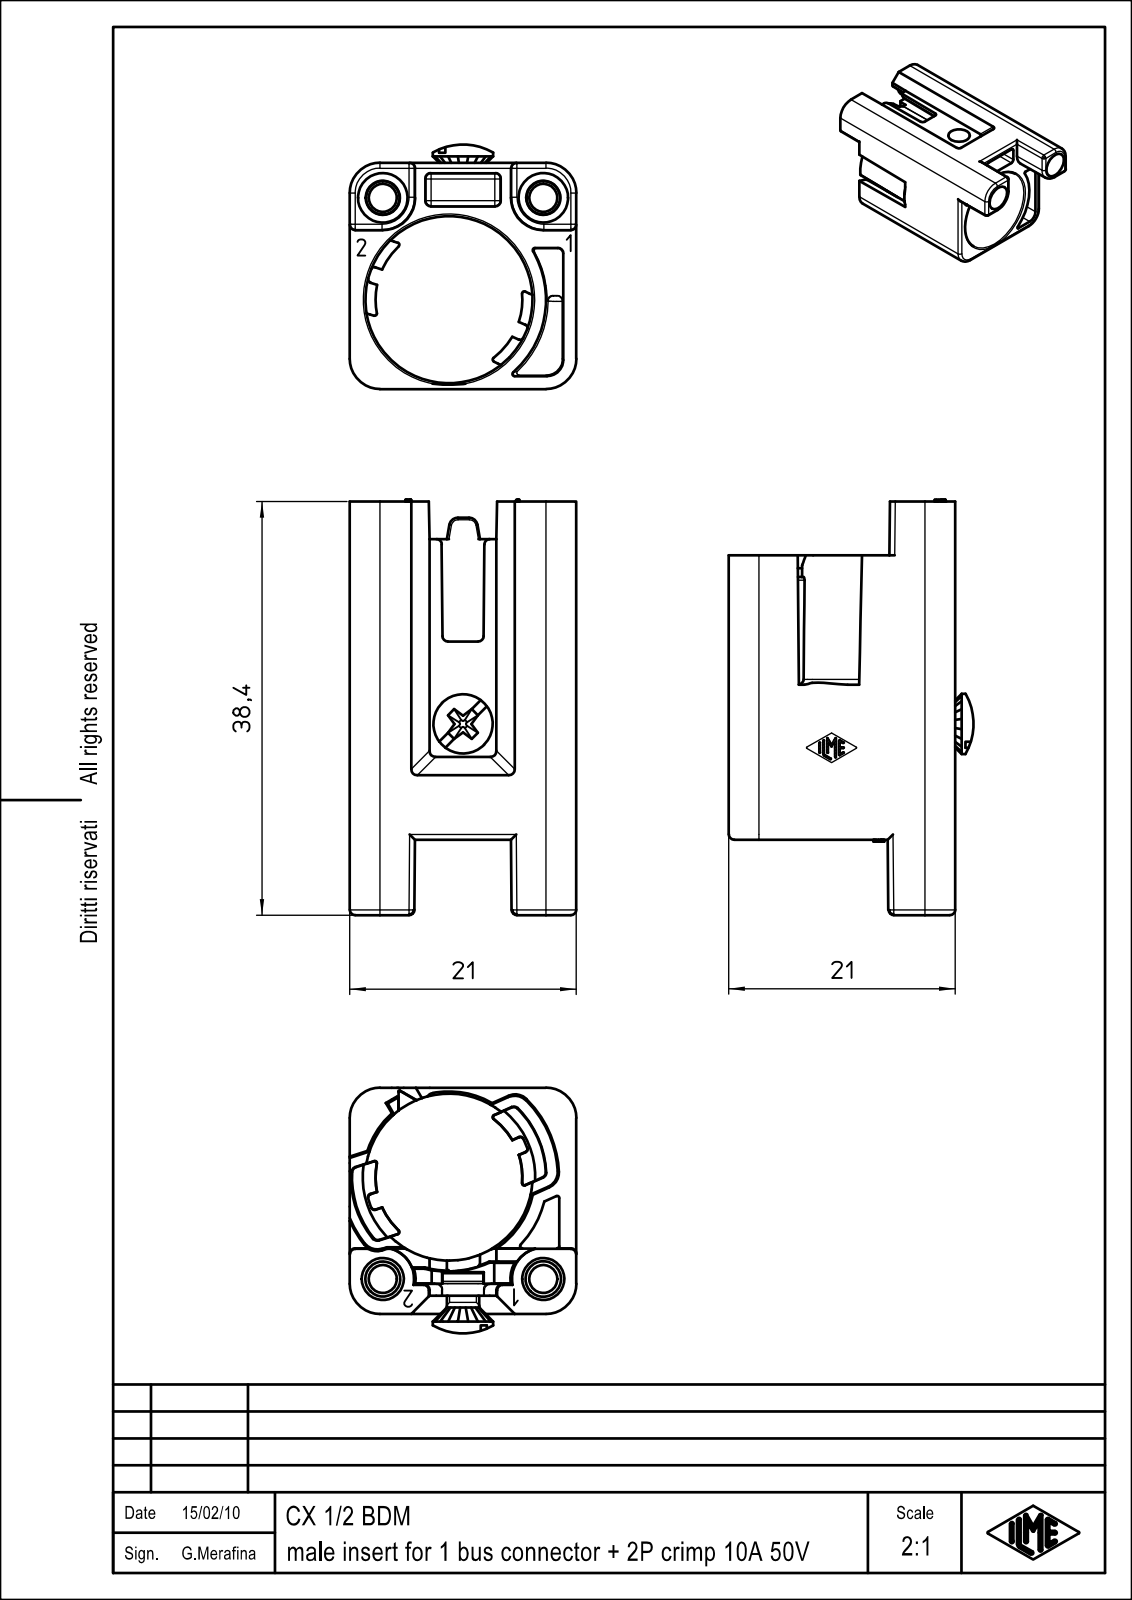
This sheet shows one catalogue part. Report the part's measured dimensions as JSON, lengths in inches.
{"part_name": "CX_1-2_BDM", "step_written_by": "Creo Elements/Direct Modeling 18.0B 02-Dec-2011 (C) Parametric Technology GmbH (AUTOMOTIVE_DESIGN)", "units": "inches", "bodies": {"solids": 1, "faces": 340, "planar": 227, "cylindrical": 45, "other": 68}, "overall_size": [1.518, 0.893, 0.827], "volume_in3": 0.373, "surface_area_in2": 8.494, "round_holes": [[0.154, 2], [0.181, 2], [0.61, 1]], "round_bosses_or_shafts": [[0.22, 1], [0.118, 1]], "partial_cylinders_radius": [[0.02, 15], [0.004, 5], [0.11, 4], [0.031, 2], [0.118, 2], [0.004, 1], [0.039, 1]], "face_to_face_distances": [0.827, 0.76, 0.067, 1.039, 0.197, 1.236, 0.079, 0.118, 1.157, 0.276], "hole_center_spacings": [0.444, 0.507, 0.587]}
